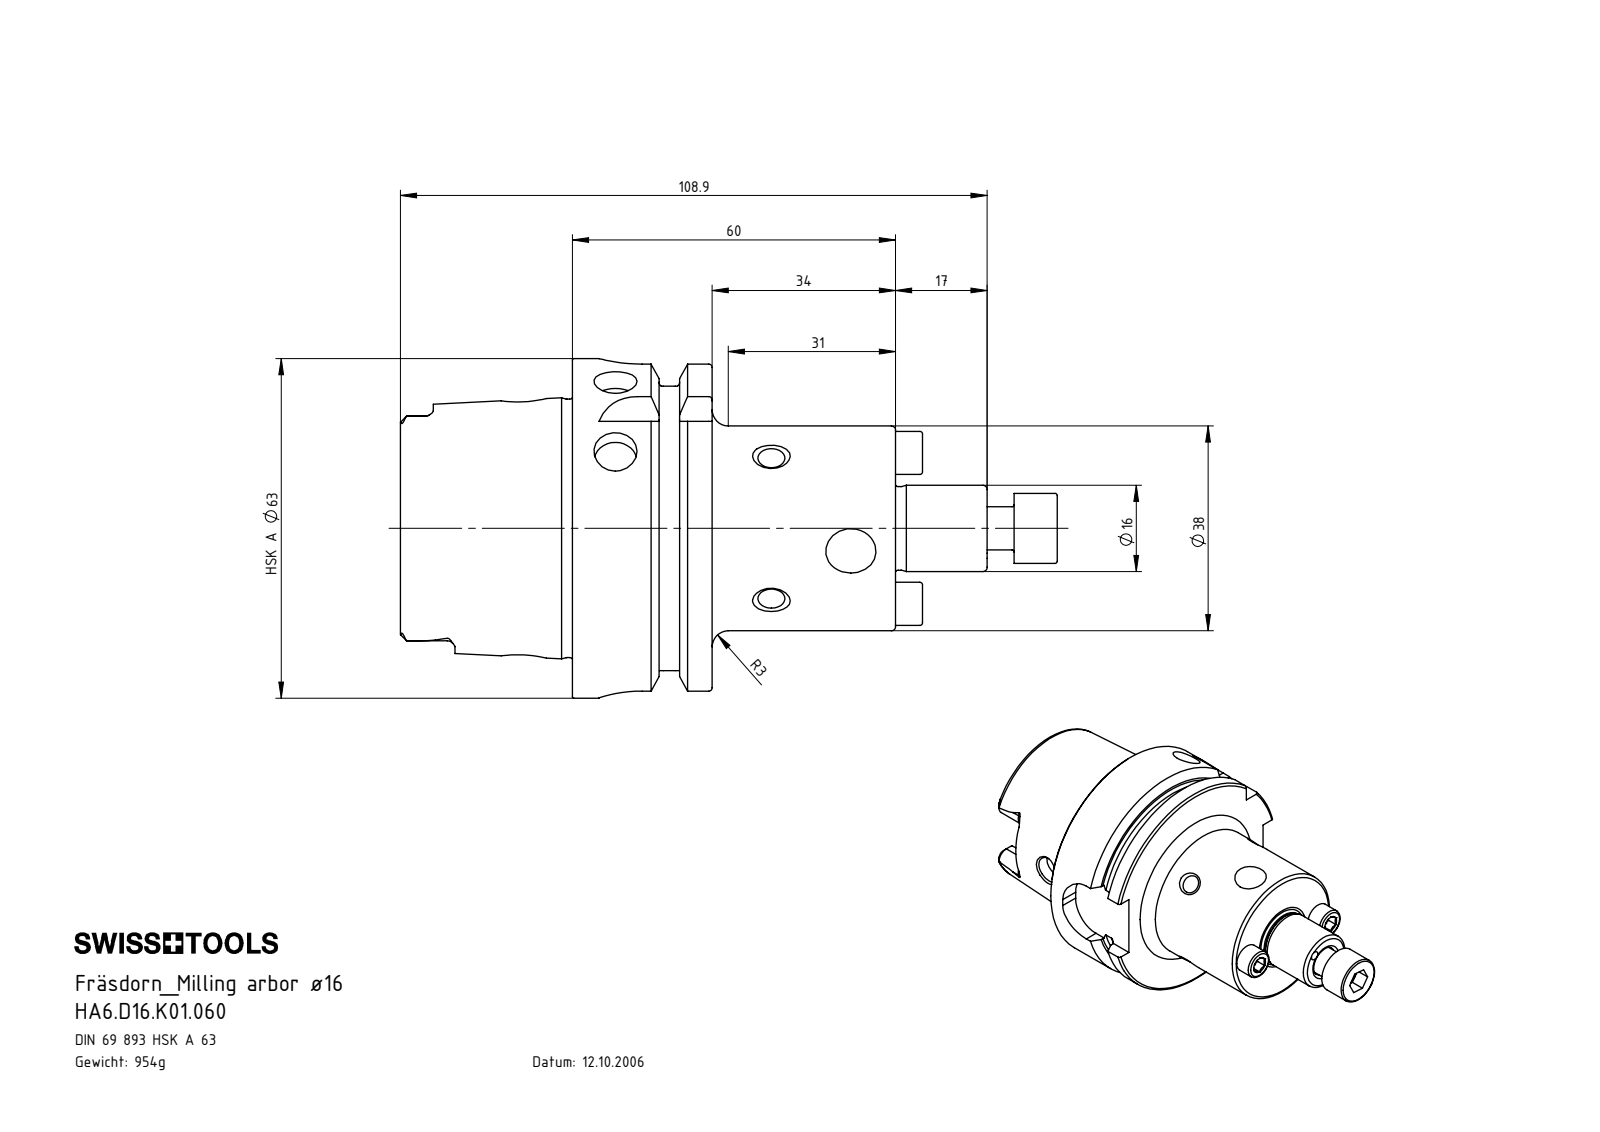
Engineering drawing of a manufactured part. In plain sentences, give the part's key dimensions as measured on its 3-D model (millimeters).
The part is named "HA6.D16.K01.060; D16-ER2.001.015_B; D16-ER1.002.025_A_Default; HA6-D16.K01.060_C_Fertigbearbeitung". Its 3-D file was written by "SolidWorks 2011 (AUTOMOTIVE_DESIGN)". It is 4 solids with 387 faces: 91 planar, 111 cylindrical and 185 other. Overall it measures 121.9 by 63 by 63 millimeters. Its volume is 121 574 cubic millimeters and its surface area 32 162 square millimeters. Round holes: 3 of diameter 2.5, 2 of diameter 3.3, 2 of diameter 5, 2 of diameter 6, 2 of diameter 8, 1 of diameter 6.8, 1 of diameter 7.5, 1 of diameter 8.4, 1 of diameter 8.5, 1 of diameter 10, 1 of diameter 17, 1 of diameter 19. Round bosses or shafts: 3 of diameter 8, 2 of diameter 4, 2 of diameter 3, 1 of diameter 63, 1 of diameter 54.95, 1 of diameter 47.94, 1 of diameter 38, 1 of diameter 16. Partial cylindrical surfaces (rounded edges, fillets, slot ends): 6 of radius 1.4, 4 of radius 2.88, 4 of radius 8, 2 of radius 2. The main face-to-face distances are 25.95, 60, 34.05, 16, 9.95, 50.05, 31.9, 41.85, 57.85, 91.9. The hole center spacings are 6.12, 10.6, 14, 18.83, 12.25, 17.05, 28.
